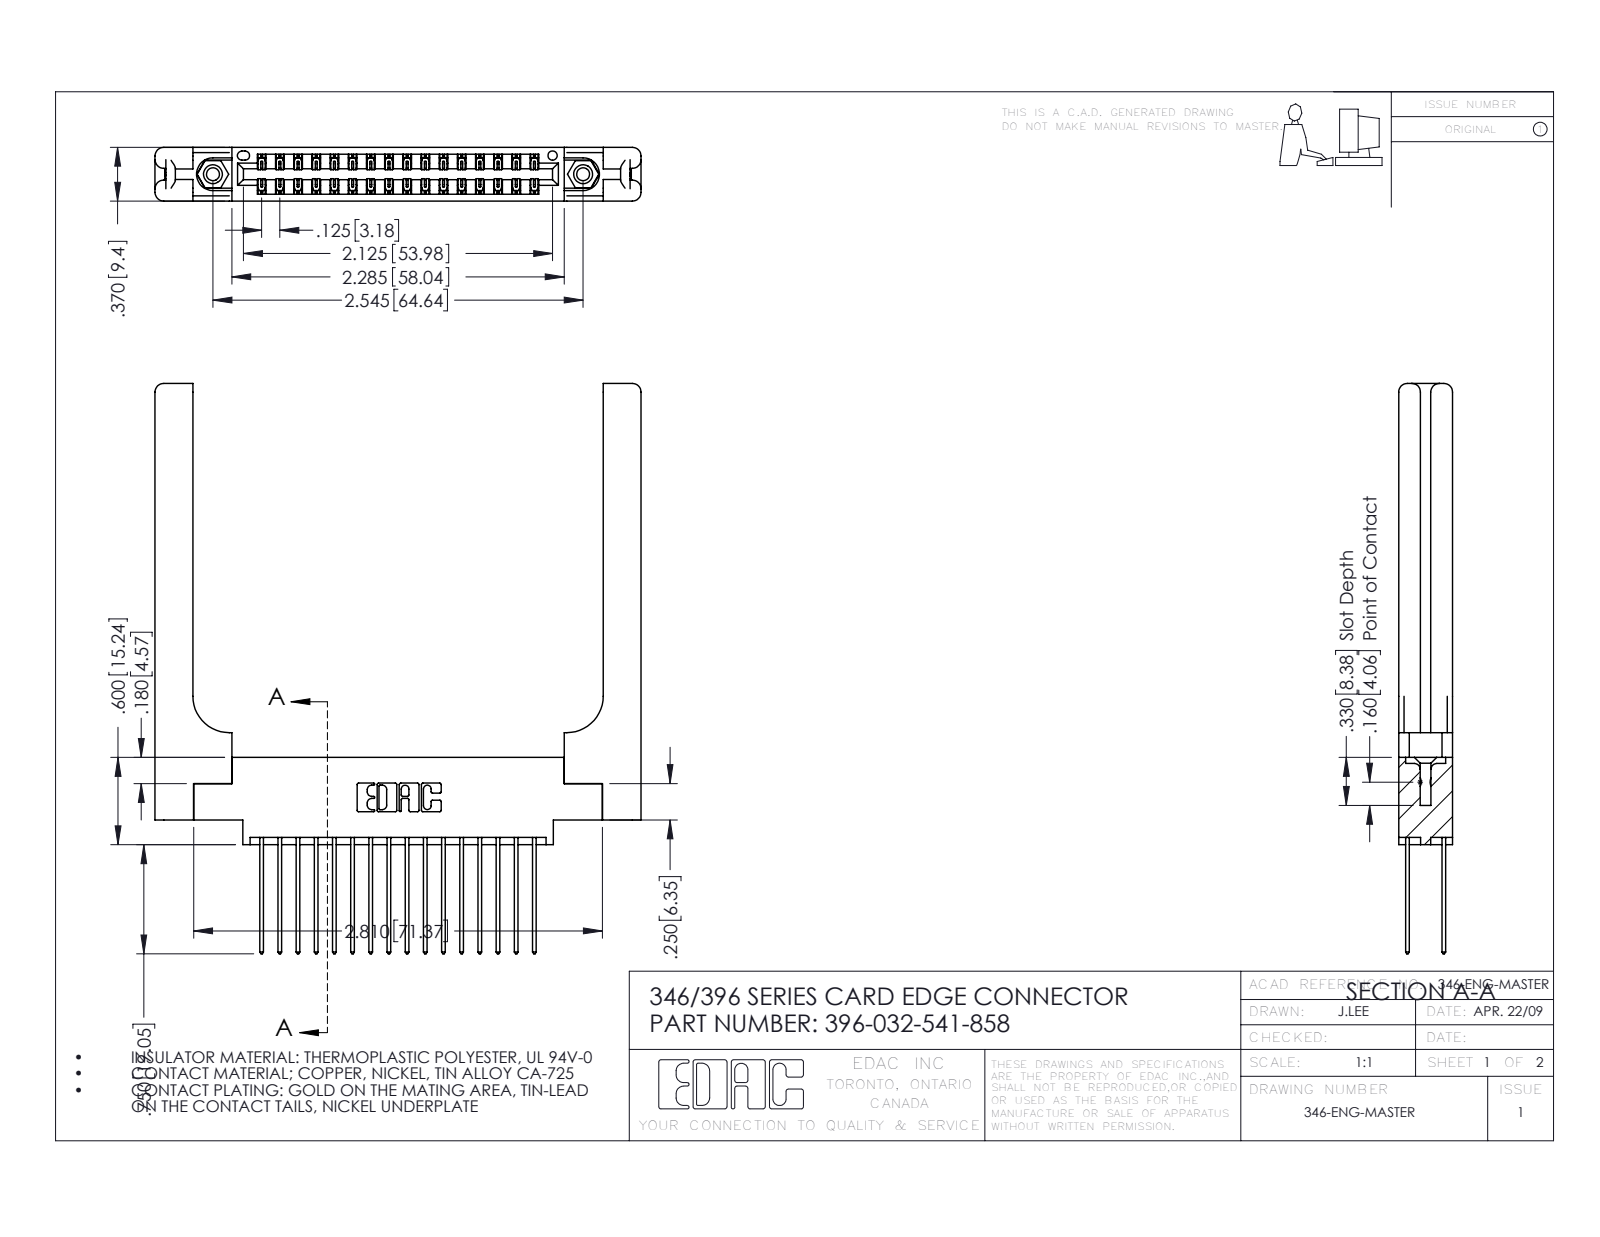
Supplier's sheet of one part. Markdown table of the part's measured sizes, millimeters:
| quantity | value |
| --- | --- |
| part name | 346 Part_0.170 Offset - 0.156 Dia-TH; 396-032-541-858; 345-292-001_345-293-141; 345-250-001_345-250-001-102 (+1 more) |
| STEP written by | SolidWorks 2016 (CONFIG_CONTROL_DESIGN) |
| units | millimeters |
| bodies | 37 solids, 2046 faces (1348 planar, 638 cylindrical, 60 other) |
| overall size | 99.6 × 84.9 × 9.4 |
| volume | 15 600 mm³ |
| surface area | 16 760 mm² |
| round holes (diameter × count) | 2.3 × 2, 3.2 × 2, 4 × 2, 1.6 × 1 |
| round bosses / shafts (diameter × count) | 3.9 × 2 |
| partial cylindrical surfaces (radius × count) | 0.2 × 48, 0.3 × 32, 0.3 × 22, 1.5 × 16, 0.2 × 6, 0.8 × 6, 0.7 × 3, 0.4 × 2 |
| main face-to-face distances | 9.4, 1.8, 1.2, 8.2, 3.8, 3.8, 6.4, 0.6, 7.6, 2 |
| hole center spacings | 6.2, 59.4, 64.6 |
